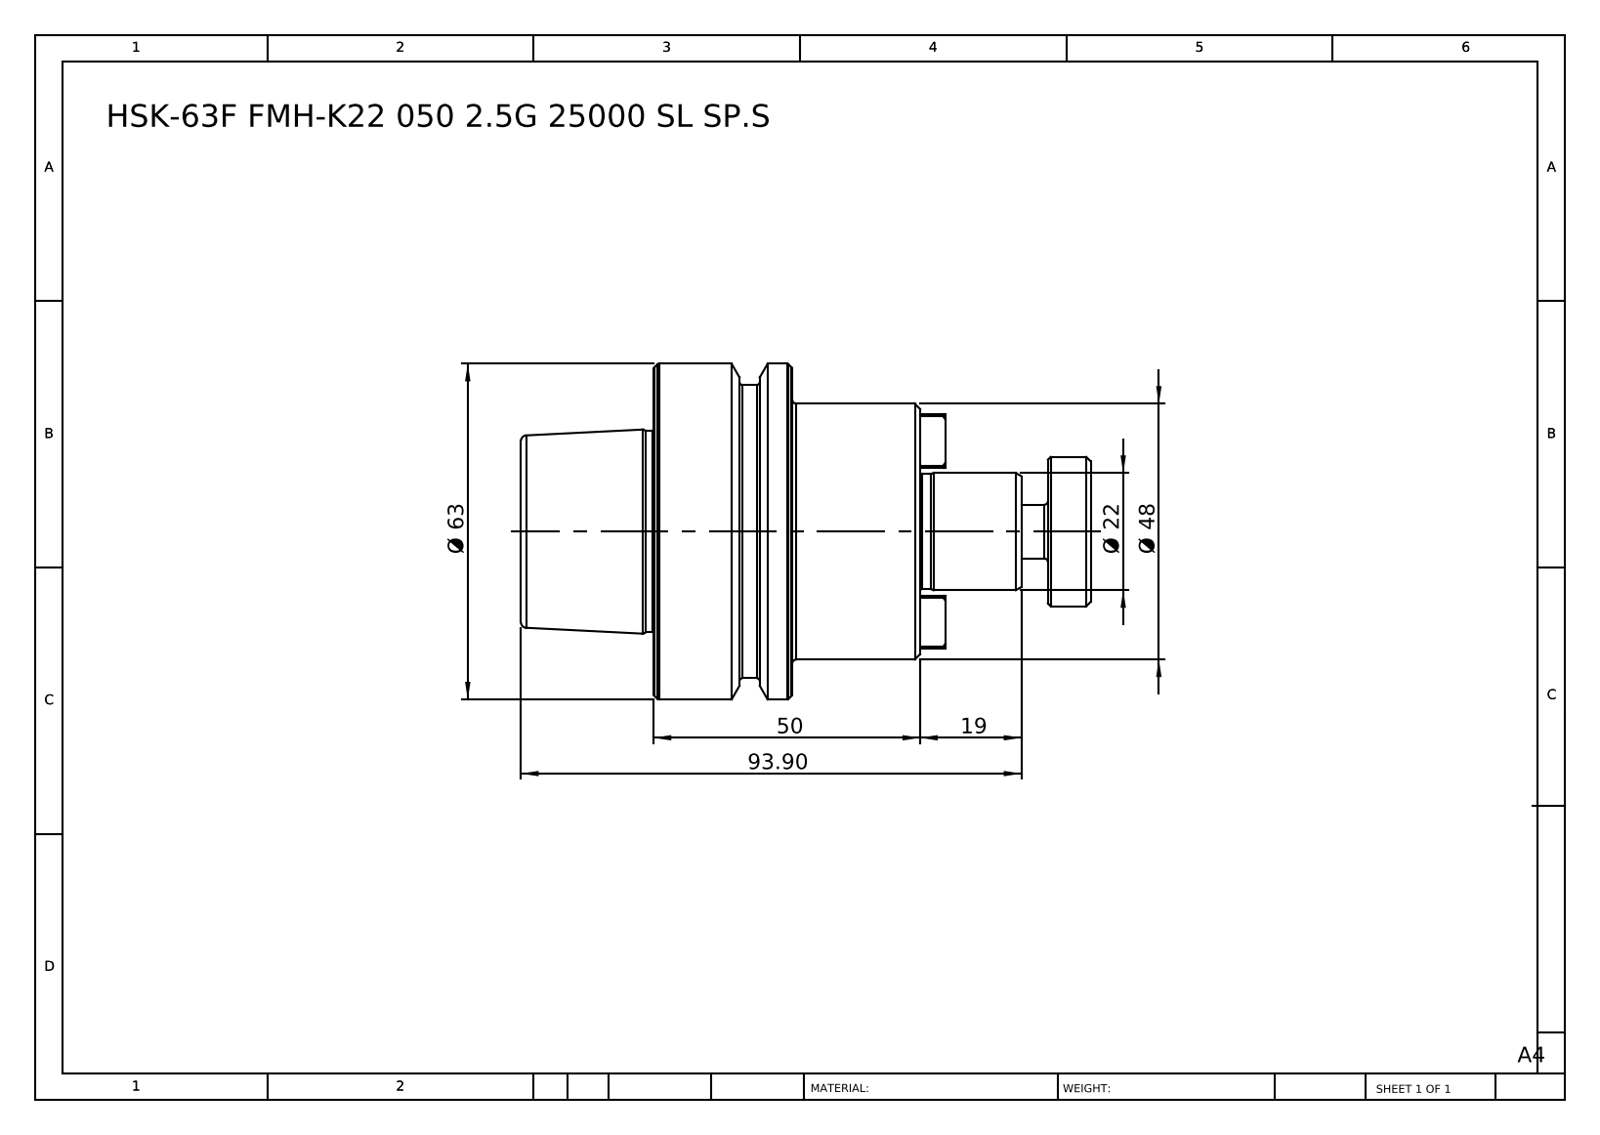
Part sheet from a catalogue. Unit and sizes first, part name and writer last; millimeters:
Units: millimetres
Overall size (bounding box): 106.9 × 63 × 63
Round bosses / shafts (diameter × count): ⌀63 ×1, ⌀55 ×1, ⌀48 ×1, ⌀37.8 ×1, ⌀28 ×1, ⌀22 ×1, ⌀21.6 ×1, ⌀10 ×1
Main face-to-face distances: 26, 24, 50, 74.9, 50.9, 24.9, 32, 56, 82, 106.9
Volume: 161 215 mm³ · Surface area: 25 703 mm²
Bodies: 2 solids, 104 faces (38 planar, 18 cylindrical, 48 other)
Part name (STEP PRODUCT): HSK-63F FMH-K22 050 2.5G 25000 SL SP
STEP written by: SolidWorks 2014 (CONFIG_CONTROL_DESIGN)
